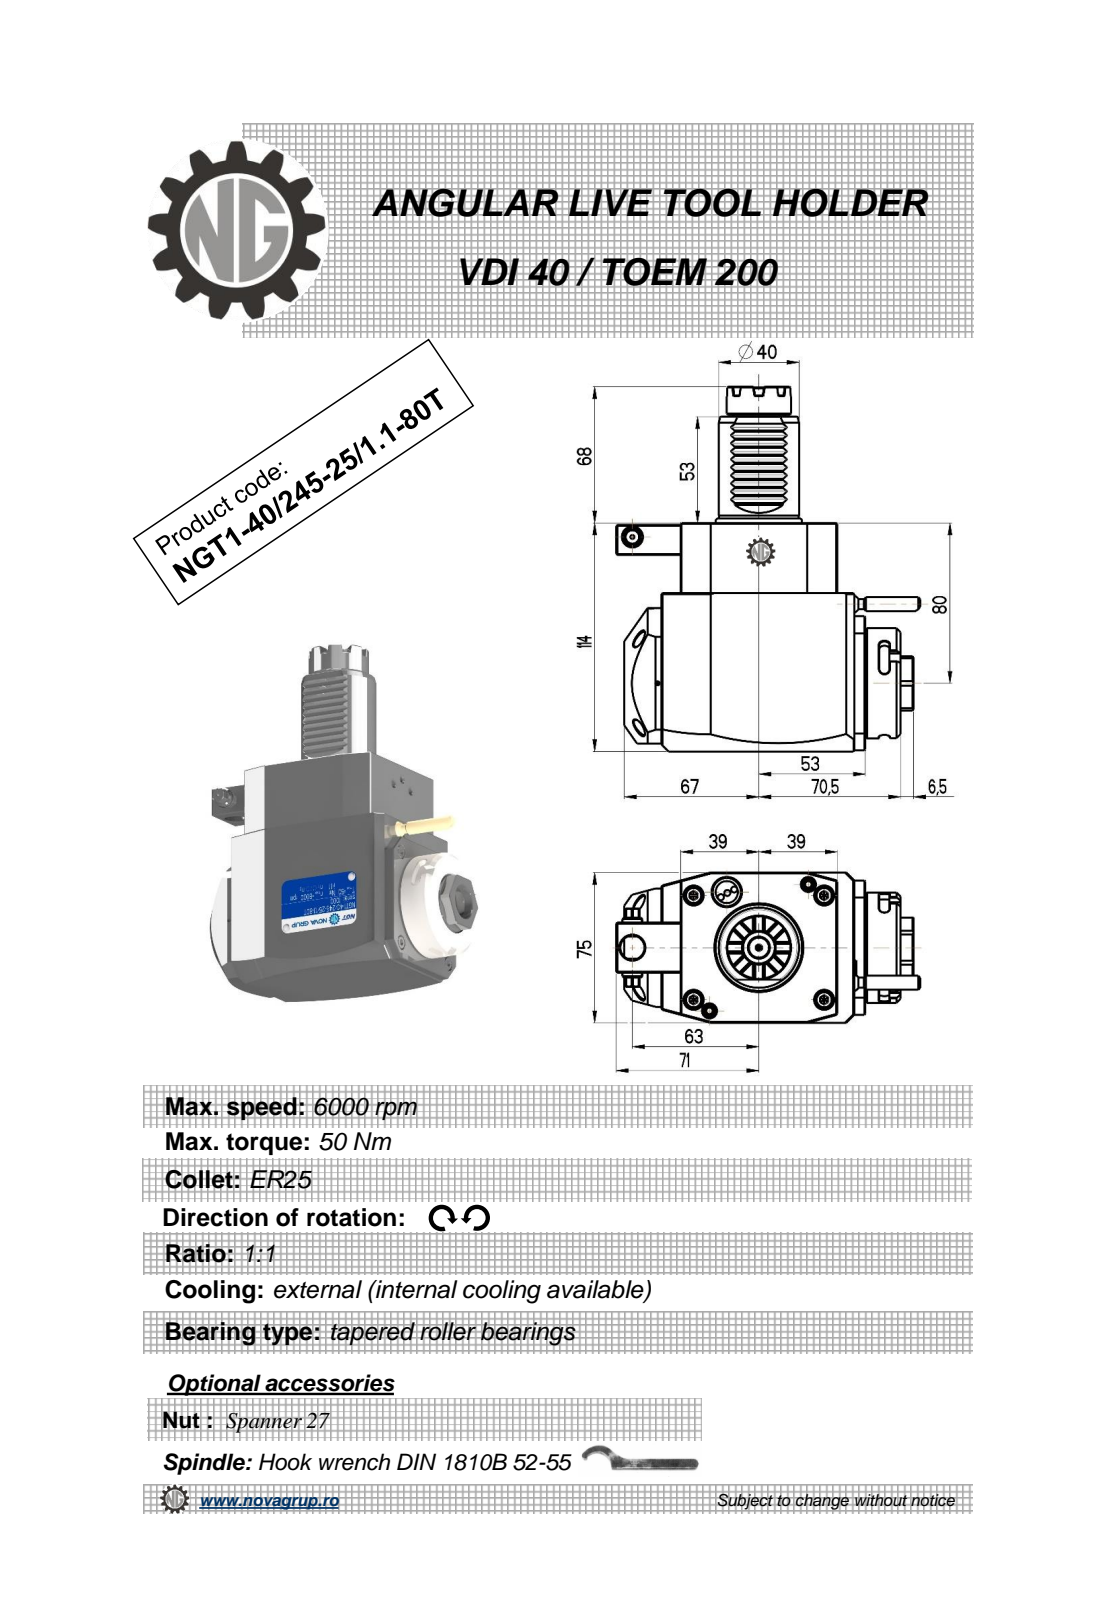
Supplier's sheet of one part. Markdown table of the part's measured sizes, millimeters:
| quantity | value |
| --- | --- |
| part name | NGT1_40_245_25_1_1_80T |
| STEP written by | PRO/ENGINEER BY PARAMETRIC TECHNOLOGY CORPORATION, 2010280 (CONFIG_CONTROL_DESIGN) |
| units | millimeters |
| bodies | 1 solid, 426 faces (222 planar, 90 cylindrical, 114 other) |
| overall size | 182 × 151.33 × 75 |
| volume | 955 782 mm³ |
| surface area | 72 063 mm² |
| round holes (diameter × count) | 2 × 1, 2.5 × 1, 3 × 1, 4.5 × 1, 9.5 × 1, 12 × 1, 18 × 1 |
| round bosses / shafts (diameter × count) | 8 × 2, 55 × 1, 48 × 1, 40 × 1, 32 × 1, 17.2 × 1, 10 × 1, 7 × 1 |
| partial cylindrical surfaces (radius × count) | 0.3 × 10, 2.5 × 6, 180 × 2, 0.5 × 1, 3.85 × 1, 4.25 × 1, 15 × 1, 24.5 × 1 |
| main face-to-face distances | 75, 114, 14, 17.5, 78, 92, 31.5, 109.5, 4, 28 |
| hole center spacings | 37.35, 43.2, 72.5 |
